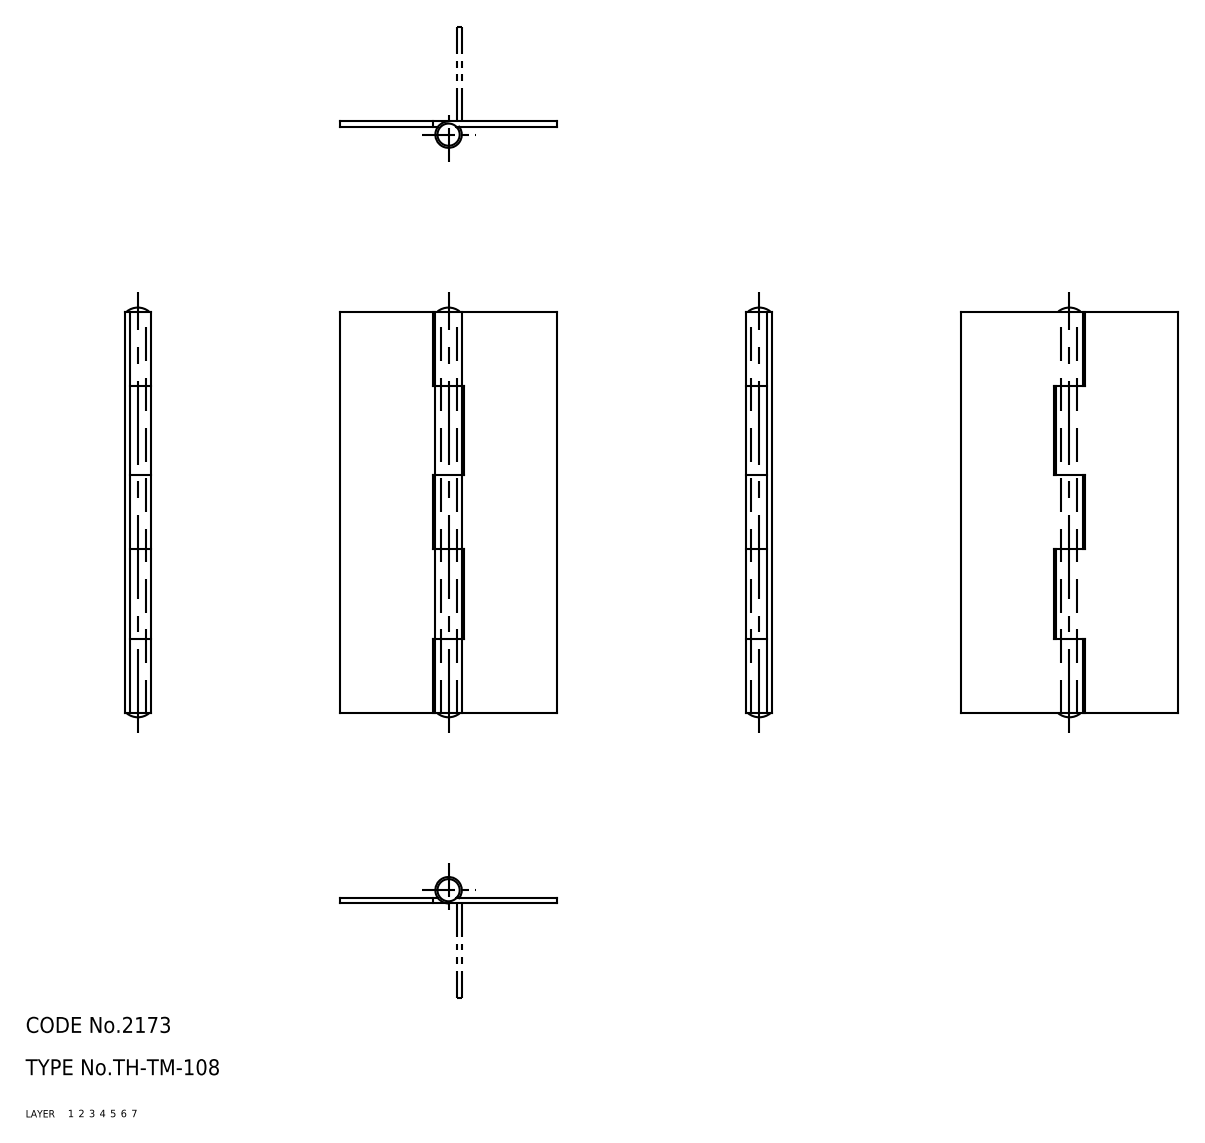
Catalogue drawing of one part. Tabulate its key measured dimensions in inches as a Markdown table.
| quantity | value |
| --- | --- |
| part name | 67110958; 67110971; 67110984 |
| STEP written by | CADfix (AUTOMOTIVE_DESIGN) |
| units | inches |
| bodies | 3 solids, 44 faces (0 planar, 0 cylindrical, 44 other) |
| overall size | 3.051 × 1.614 × 0.197 |
| volume | 0.259 in³ |
| surface area | 13.44 in² |
